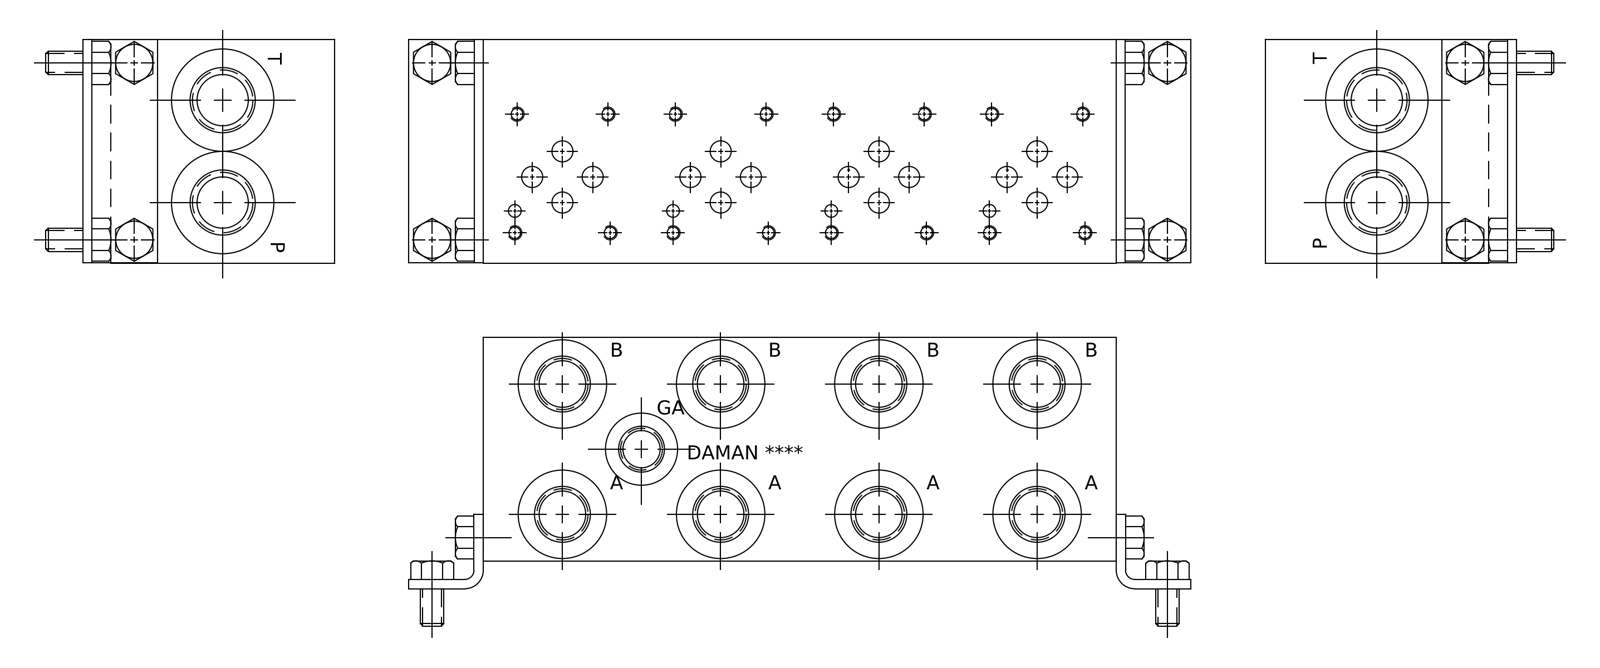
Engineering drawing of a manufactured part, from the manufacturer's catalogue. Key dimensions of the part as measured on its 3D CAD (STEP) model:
Part name (STEP PRODUCT): Part_DD03P042S_3D
STEP written by: Autodesk Inventor 2019 (AUTOMOTIVE_DESIGN)
Units: millimetres
Bodies: 1 solid, 831 faces (428 planar, 128 cylindrical, 275 other)
Overall size (bounding box): 215.9 × 76.2 × 76.2
Volume: 1 147 000 mm³ · Surface area: 104 151 mm²
Round holes (diameter × count): ⌀3.78 ×16, ⌀4.83 ×16, ⌀7.14 ×12, ⌀14.3 ×8, ⌀17.5 ×8, ⌀19.05 ×8, ⌀19.25 ×8, ⌀30.63 ×8, ⌀3.96 ×4, ⌀6.35 ×4, ⌀6.53 ×2, ⌀7.92 ×2
Main face-to-face distances: 76.2, 0.79, 215.9, 75.41, 215.11, 214.32, 15.06, 14.27, 61.14, 1
Hole centre spacings: 107.95, 53.98, 53.97, 161.93, 19.95, 22.05, 33.55, 51.45
